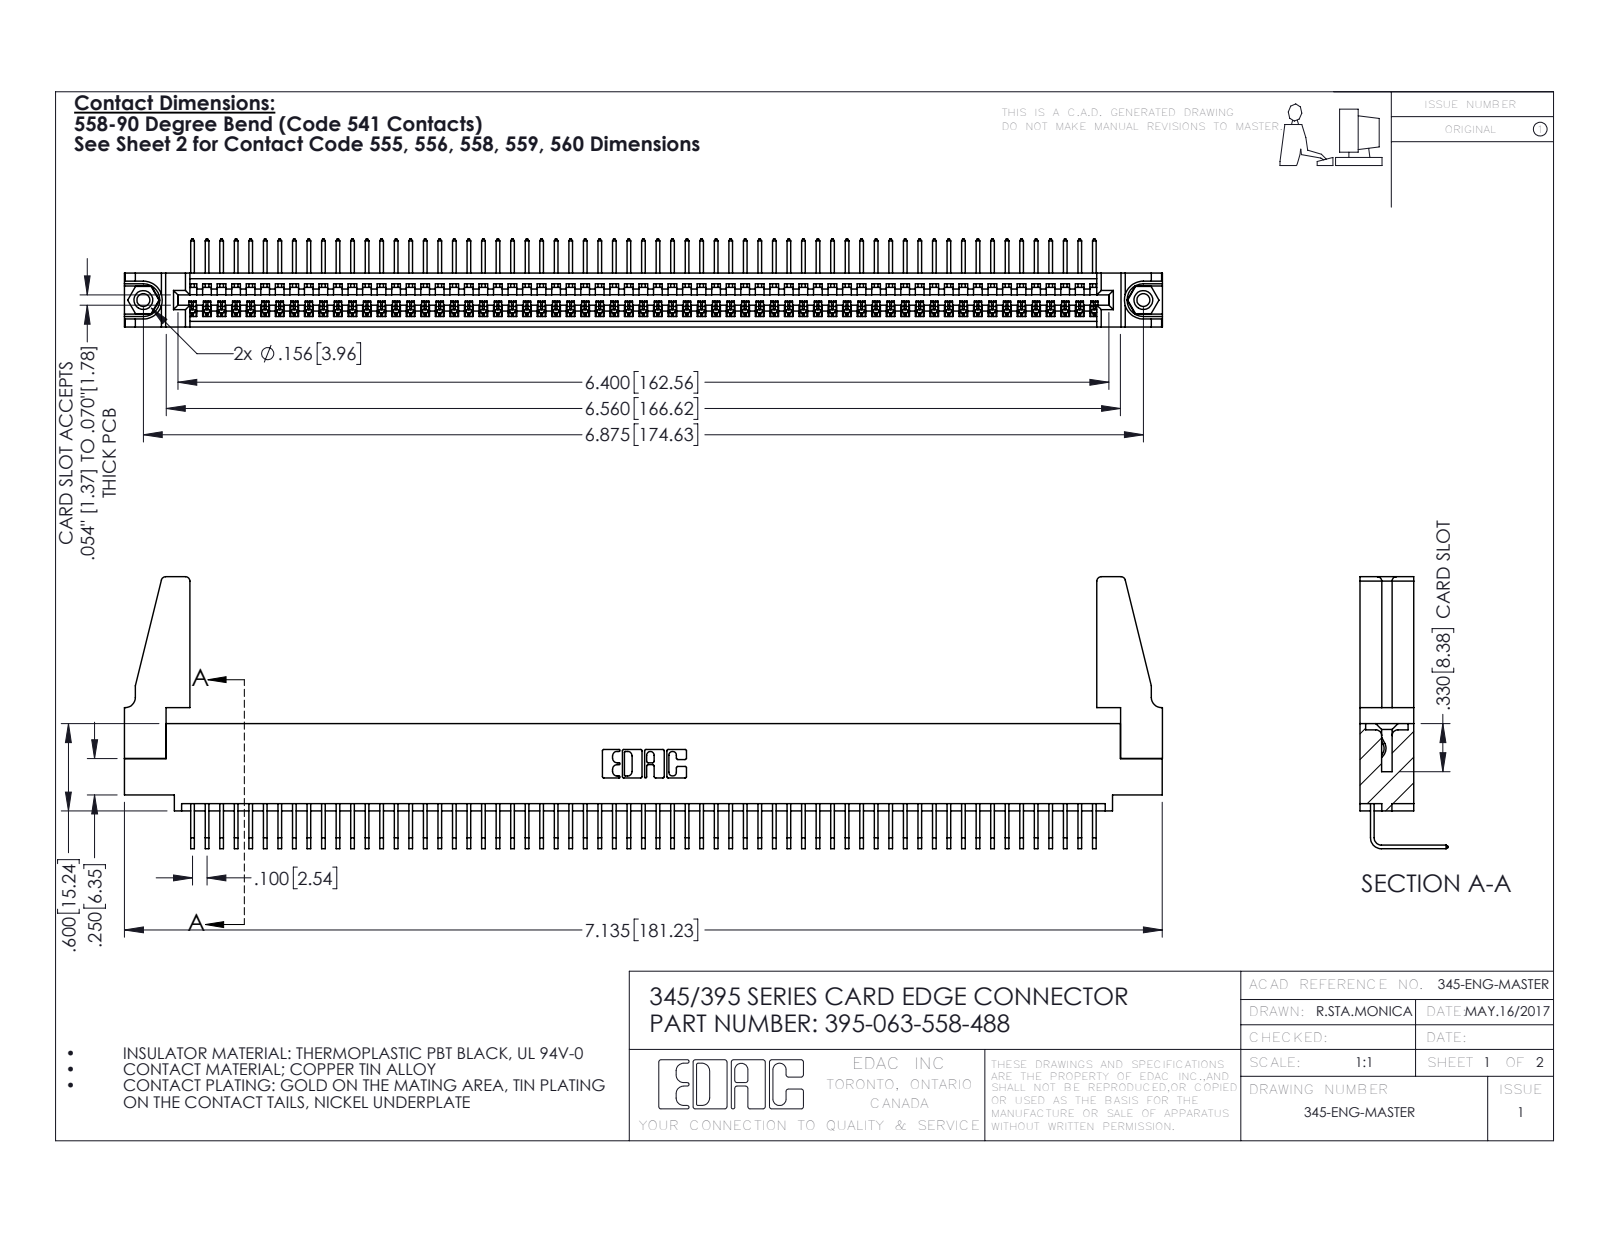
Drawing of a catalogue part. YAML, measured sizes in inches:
part_name: "345-292-001_558 Tail - 2; 345-250-001_345-250-001-102; 345 Part_0.110 Offset - 0.156 Dia-TH; 345-220-078_345-220-088 (+1 more)"
step_written_by: "SolidWorks 2016 (CONFIG_CONTROL_DESIGN)"
units: inches
bodies: {solids: 68, faces: 4034, planar: 2802, cylindrical: 1216, other: 16}
overall_size: [7.136, 1.869, 0.605]
volume: 1.268
surface_area: 43.43
round_holes:
  - {diameter: 0.089, count: 2}
  - {diameter: 0.125, count: 2}
  - {diameter: 0.156, count: 2}
  - {diameter: 0.064, count: 1}
round_bosses_or_shafts:
  - {diameter: 0.155, count: 2}
partial_cylinders:
  - {radius: 0.006, count: 126}
  - {radius: 0.01, count: 22}
  - {radius: 0.03, count: 8}
  - {radius: 0.007, count: 6}
  - {radius: 0.031, count: 6}
  - {radius: 0.026, count: 3}
  - {radius: 0.031, count: 2}
  - {radius: 0.04, count: 2}
face_to_face_distances: [0.072, 0.298, 0.37, 0.2, 0.098, 0.272, 0.025, 0.225, 0.149, 0.072]
hole_center_spacings: [0.27, 6.639, 6.875]
